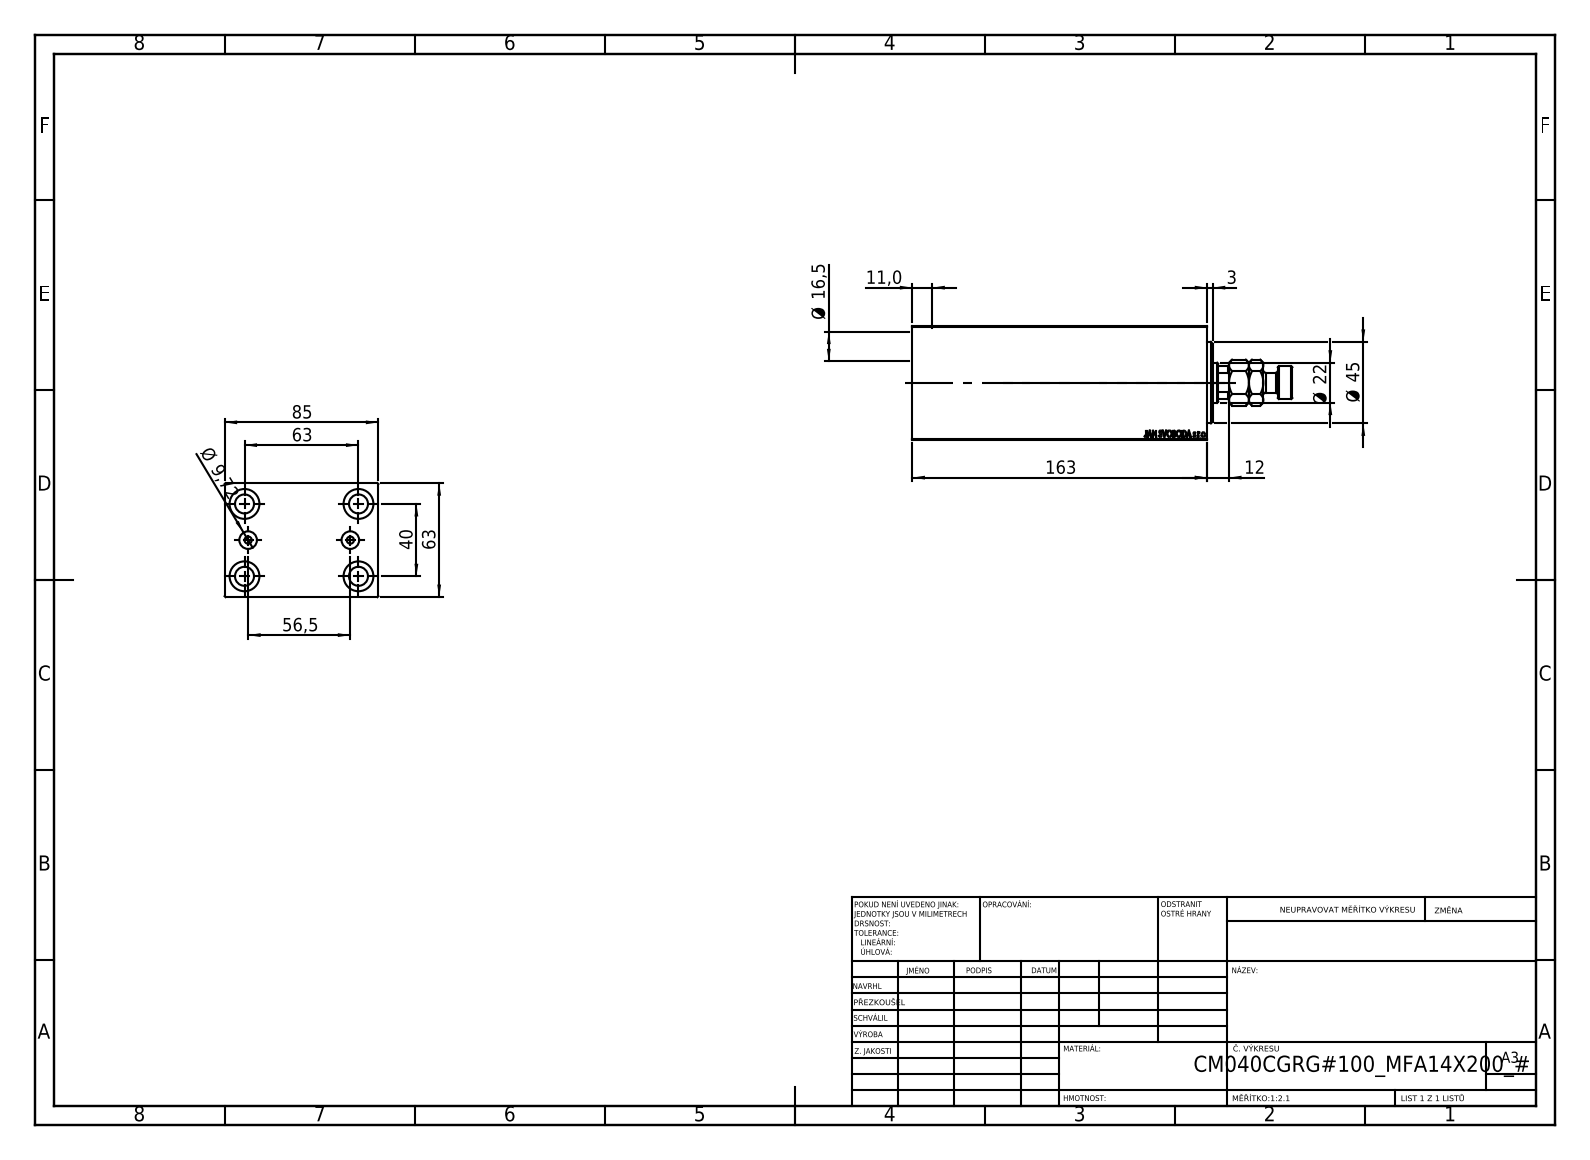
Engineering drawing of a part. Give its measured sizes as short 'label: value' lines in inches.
name: V450CM_C_VCP; V450CM_C_Body; V450CM_VC_B; MFA
written by: SolidWorks 2019 (CONFIG_CONTROL_DESIGN)
unit: in
bodies: 4 solids, 910 faces (424 planar, 60 cylindrical, 426 other)
size: 8.268 × 3.346 × 2.48
volume: 44.42 in³; area: 201.7 in²
holes: 4× ⌀0.413, 4× ⌀0.65, 2× ⌀0.157, 2× ⌀0.383, 1× ⌀0.492, 1× ⌀0.866, 1× ⌀1.004, 1× ⌀1.575, 1× ⌀1.654, 1× ⌀1.772
bosses: 1× ⌀0.709, 1× ⌀0.433
rounds: 1× R0.413
face distances: 2.48, 3.346, 0.472, 5.945, 6.417, 0.039, 5.472, 0.433, 5.984, 5.512
hole spacings: 1.469, 0.791, 0.807, 1.575, 2.434, 2.48, 2.528, 2.938
